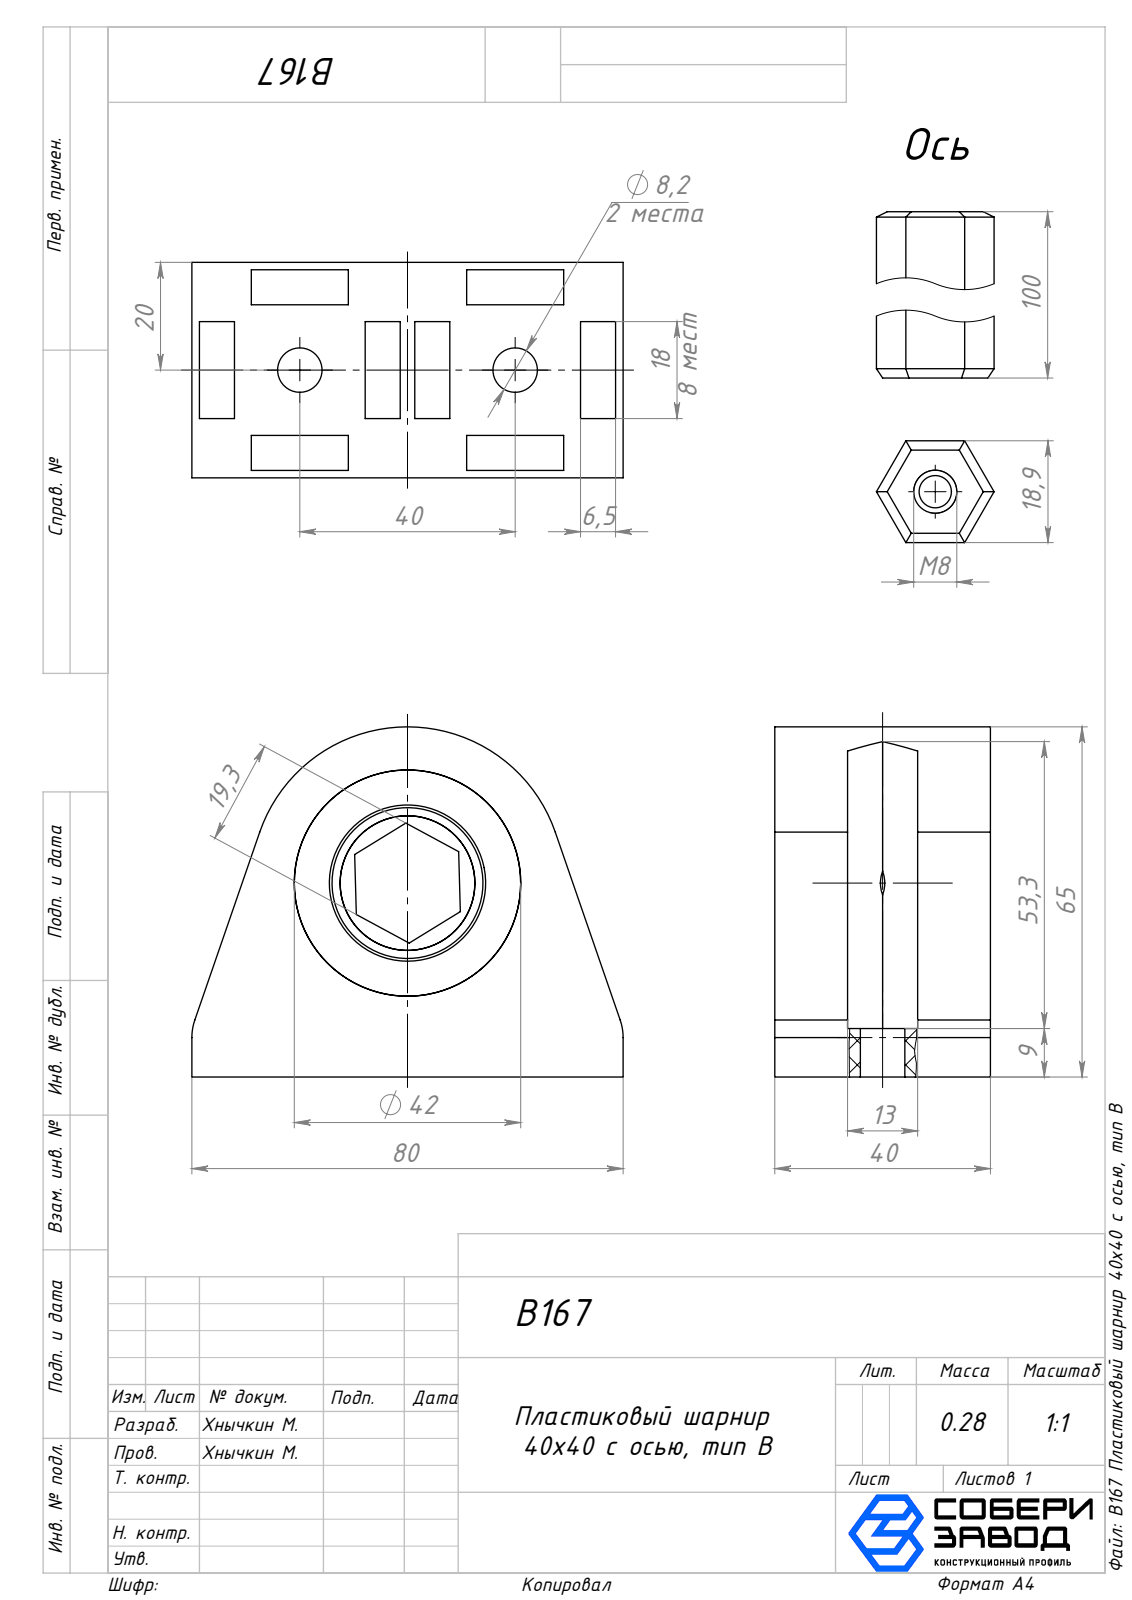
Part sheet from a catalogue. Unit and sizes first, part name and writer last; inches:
Units: inches
Overall size (bounding box): 3.937 × 3.15 × 2.559
Round holes (diameter × count): ⌀0.325 ×2, ⌀0.236 ×1, ⌀0.984 ×1, ⌀1.142 ×1, ⌀1.654 ×1
Round bosses / shafts (diameter × count): ⌀1.102 ×1
Partial cylindrical surfaces — rounded edges, fillets, slot ends (radius × count): R0.394 ×2, R1.142 ×1
Main face-to-face distances: 0.177, 0.354, 1.22, 1.575, 0.744, 0.531, 1.043, 0.689, 0.752, 0.866
Hole centre spacings: 1.572
Volume: 8.897 in³ · Surface area: 77.13 in²
Bodies: 5 solids, 146 faces (101 planar, 41 cylindrical, 4 other)
Part name (STEP PRODUCT): B167 Подшипник_00; B167 Корпус_00; B167 Пластиковый шарнир 40х40 с осью, тип B; B167 Цилиндр_00 (+1 more)
STEP written by: SolidWorks 2025 (AUTOMOTIVE_DESIGN)
